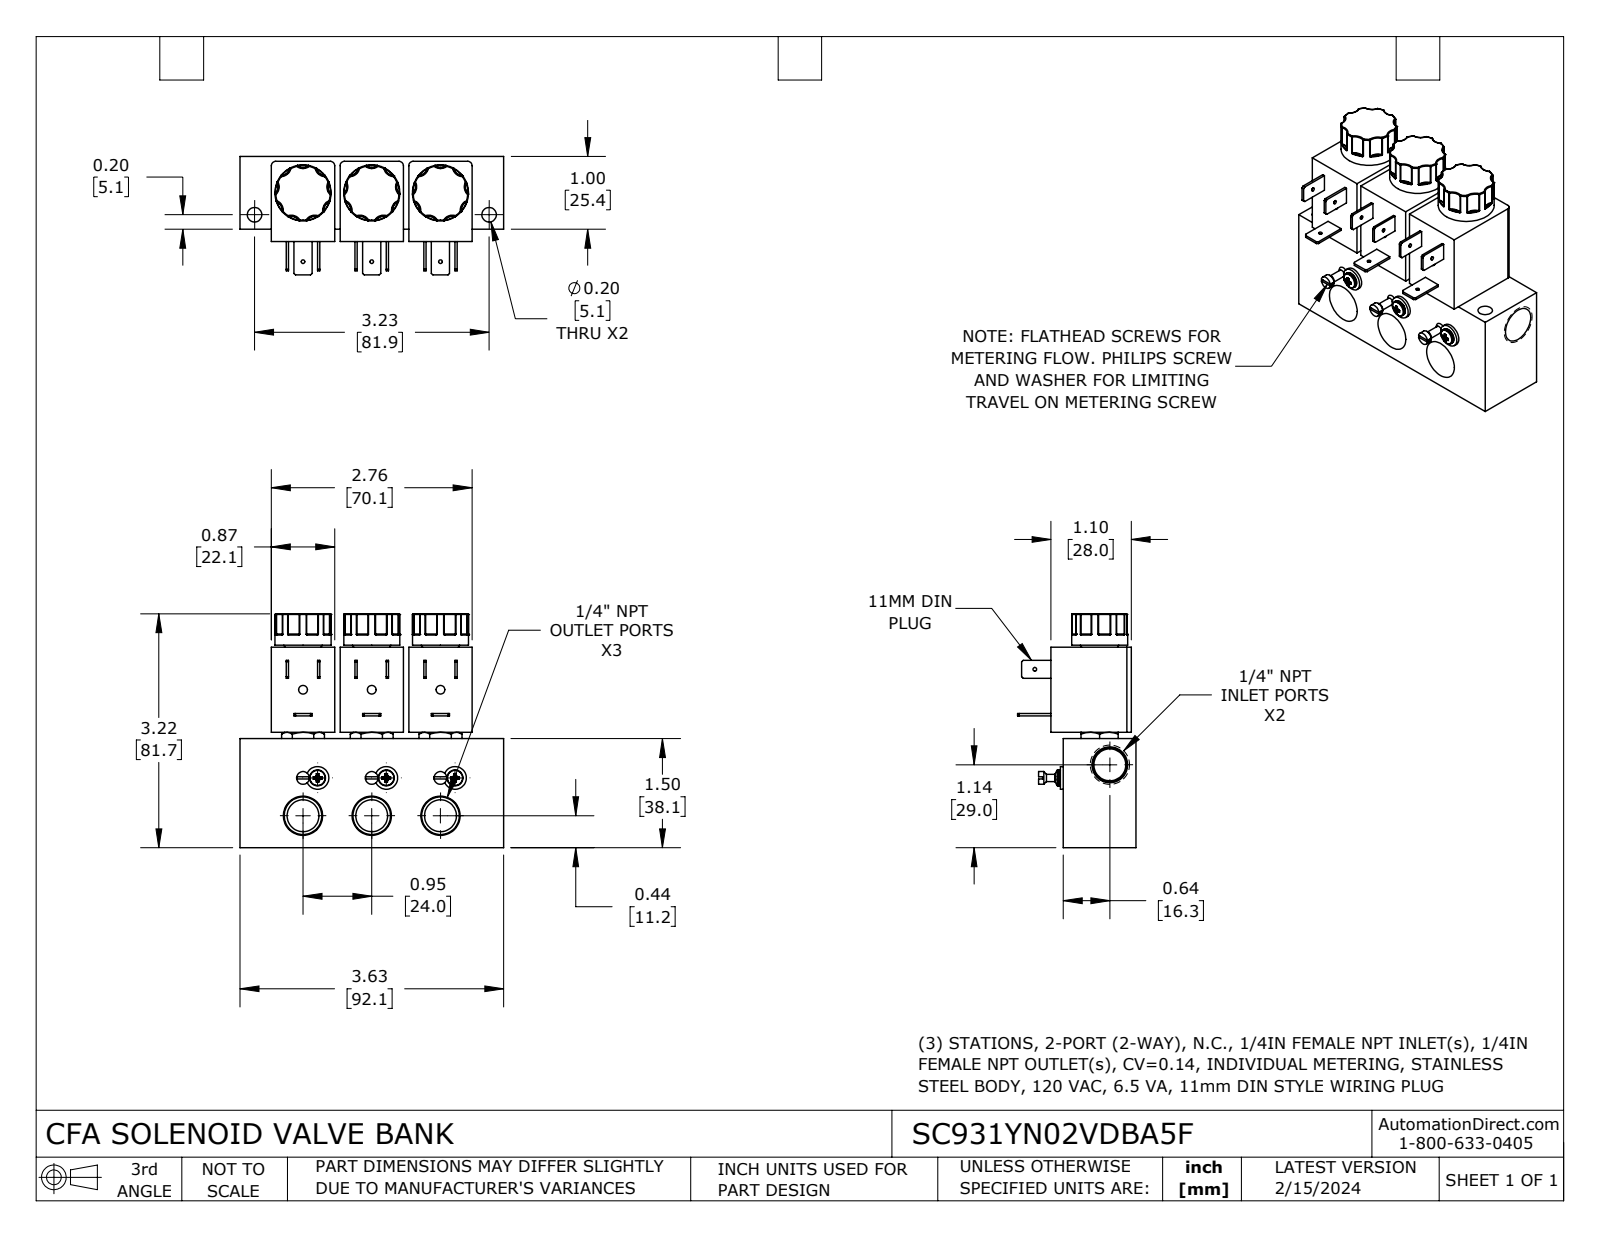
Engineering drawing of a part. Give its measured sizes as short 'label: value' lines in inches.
name: SC931YN02VDBA5F
written by: SolidWorks 2023 (CONFIG_CONTROL_DESIGN)
unit: in
bodies: 1 solid, 829 faces (215 planar, 197 cylindrical, 417 other)
size: 3.625 × 3.215 × 1.627
volume: 8.838 in³; area: 53.67 in²
holes: 4× ⌀0.05, 4× ⌀0.438, 3× ⌀0.12, 2× ⌀0.2
bosses: 3× ⌀0.77, 3× ⌀0.312, 3× ⌀0.219, 3× ⌀0.175, 3× ⌀0.1
rounds: 54× R0.01, 27× R0.133, 6× R0.06
face distances: 1, 0.945, 1.169, 0.169, 1.5, 0.945, 1.89, 0.065, 0.935, 1.104
hole spacings: 0.945, 0.945, 1.732, 1.89, 1.973, 1.973, 2.564, 0.928
